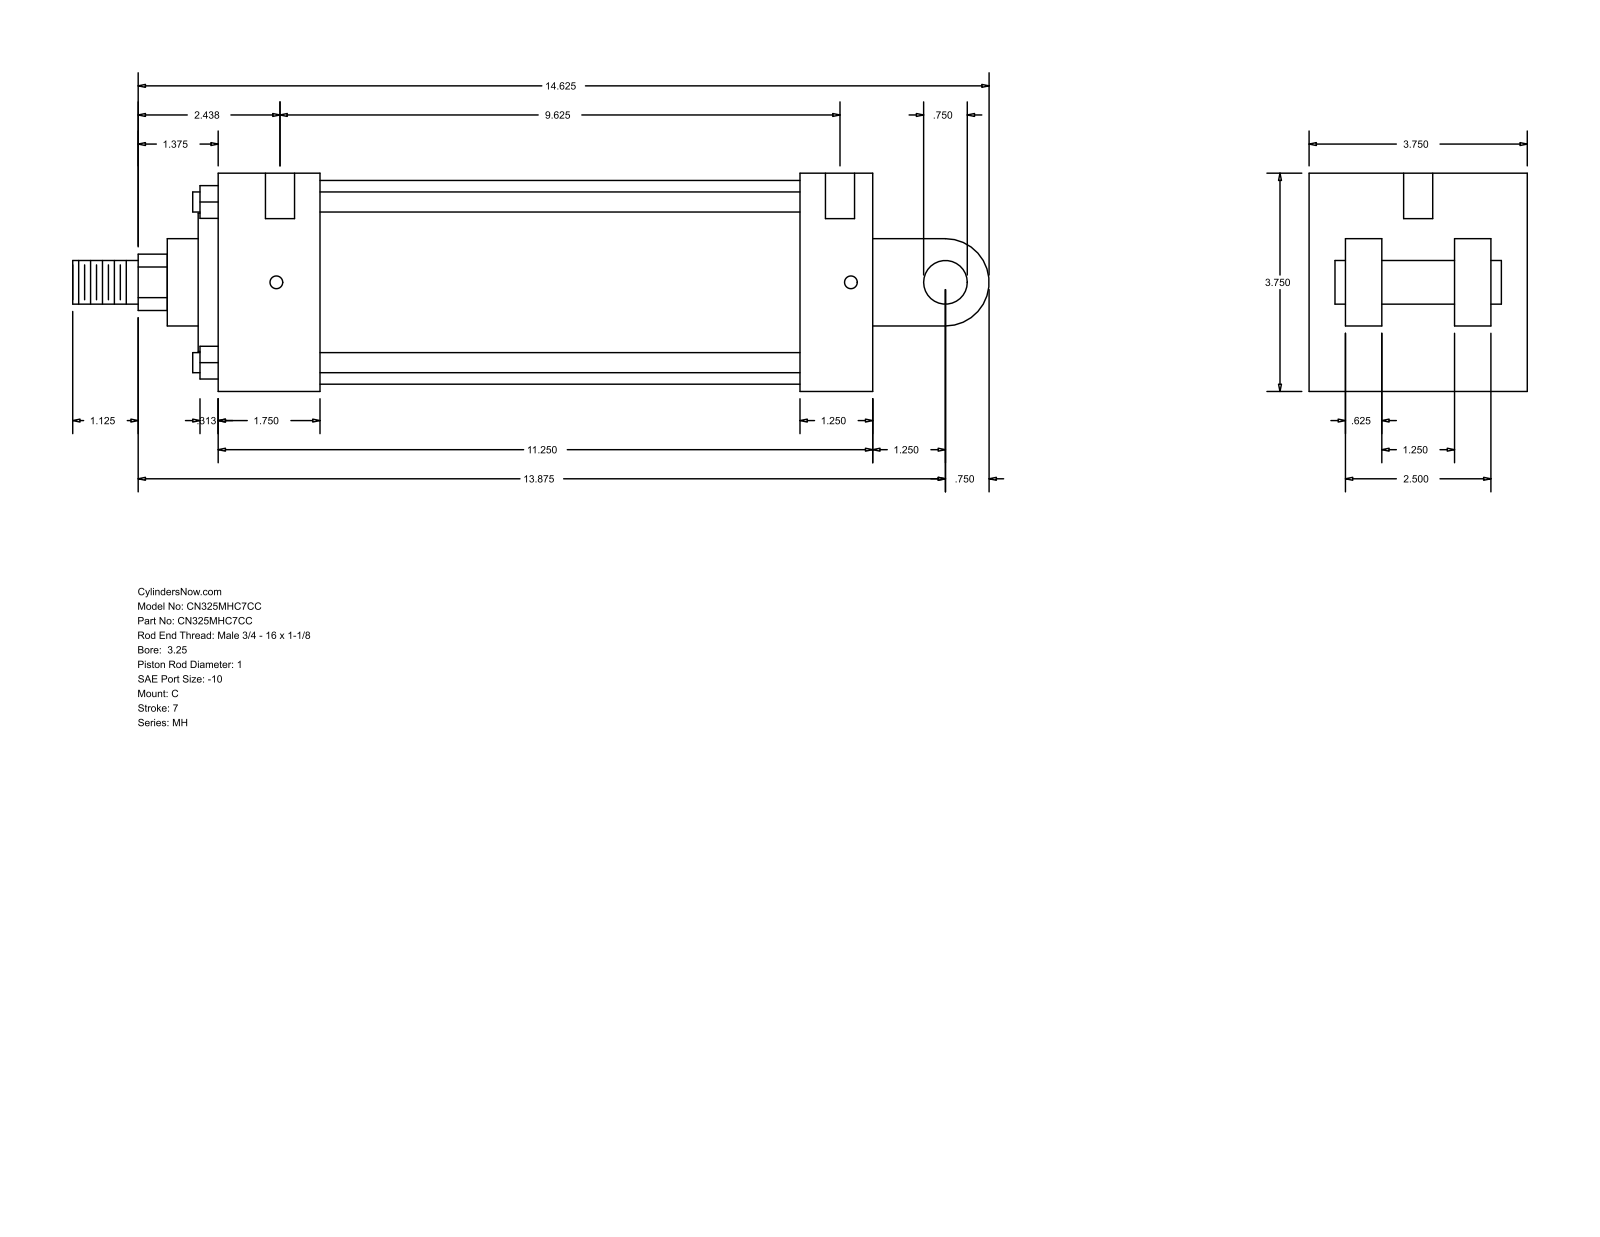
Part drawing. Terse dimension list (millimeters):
name: MH_C__0325_1
written by: GSSL Pune (CONFIG_CONTROL_DESIGN)
unit: mm
bodies: 0 solids, 101 faces (71 planar, 30 cylindrical, 0 other)
size: 400.05 × 95.25 × 95.25
holes: 4× ⌀5.56, 2× ⌀12.7
bosses: 4× ⌀8.76, 2× ⌀19.05, 1× ⌀88.9, 1× ⌀60.33, 1× ⌀38.1, 1× ⌀25.4
rounds: 1× R12.29, 1× R19.05
face distances: 95.24, 15.87, 285.76, 63.5, 79.37, 31.74, 47.63, 44.46, 254.01, 209.55
hole spacings: 250.82, 1.58, 4.76, 244.48, 246.06, 249.24
